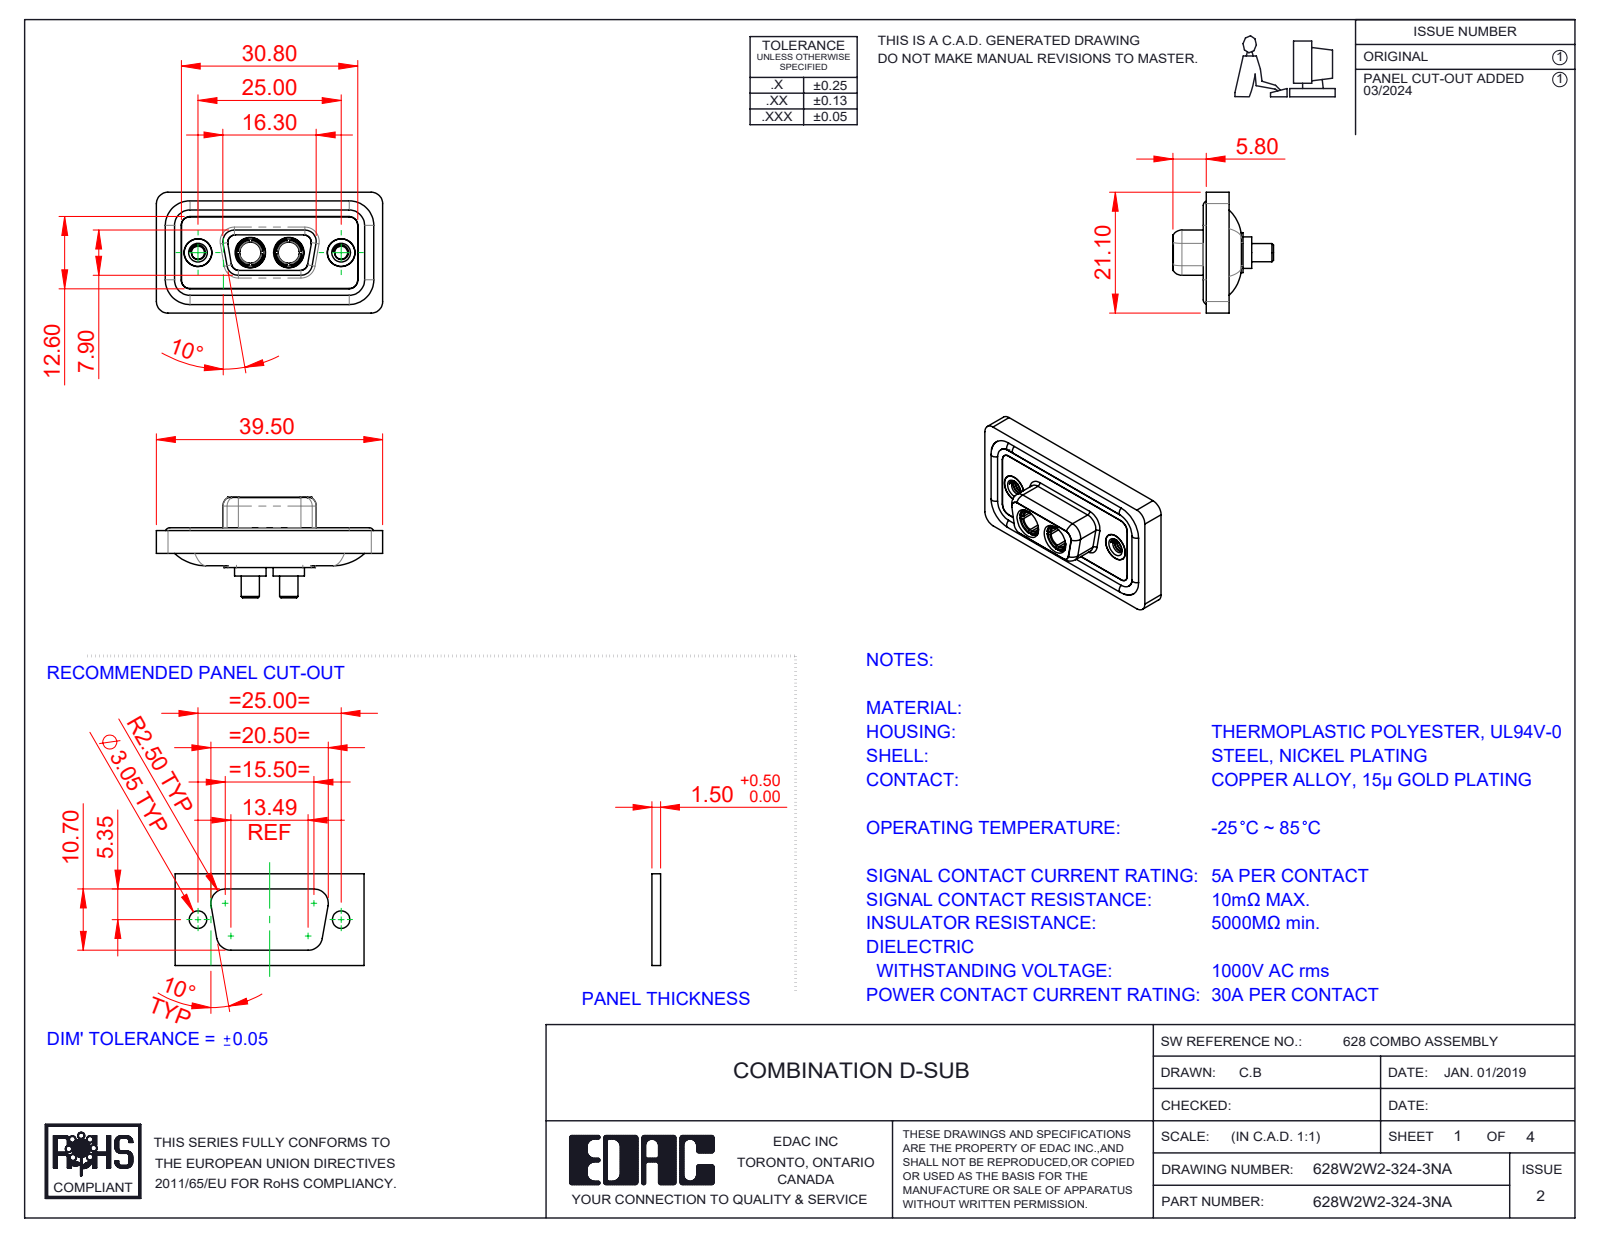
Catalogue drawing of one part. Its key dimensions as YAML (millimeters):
part_name: "628Combo Shell Front_09 Contacts; 628Combo Threaded Rivet_A; Power Socket_30A S; 628Combo Waterproof Housing_09 Contacts (+3 more)"
step_written_by: "SolidWorks 2023 (CONFIG_CONTROL_DESIGN)"
units: millimeters
bodies: {solids: 11, faces: 532, planar: 163, cylindrical: 236, other: 133}
overall_size: [39.5, 21.1, 17.55]
volume: 4729
surface_area: 7643
round_holes:
  - {diameter: 4.85, count: 4}
  - {diameter: 2.26, count: 2}
  - {diameter: 3.7, count: 2}
  - {diameter: 4, count: 2}
  - {diameter: 4.05, count: 2}
  - {diameter: 5, count: 2}
  - {diameter: 5.3, count: 2}
round_bosses_or_shafts:
  - {diameter: 1.6, count: 4}
  - {diameter: 5.5, count: 2}
  - {diameter: 5.2, count: 2}
  - {diameter: 4.96, count: 2}
  - {diameter: 4.95, count: 2}
  - {diameter: 4.8, count: 2}
  - {diameter: 4.75, count: 2}
  - {diameter: 3.75, count: 2}
partial_cylinders:
  - {radius: 1.5, count: 22}
  - {radius: 2, count: 18}
  - {radius: 1.35, count: 8}
  - {radius: 1.6, count: 8}
  - {radius: 0.25, count: 4}
  - {radius: 0.5, count: 4}
  - {radius: 0.6, count: 4}
  - {radius: 0.65, count: 4}
face_to_face_distances: [0.4, 1.8, 1.1, 2.9, 0.5, 1.6, 5.65, 7.45, 1.5, 5.35]
hole_center_spacings: [9.14, 15.86, 6.72, 25]
